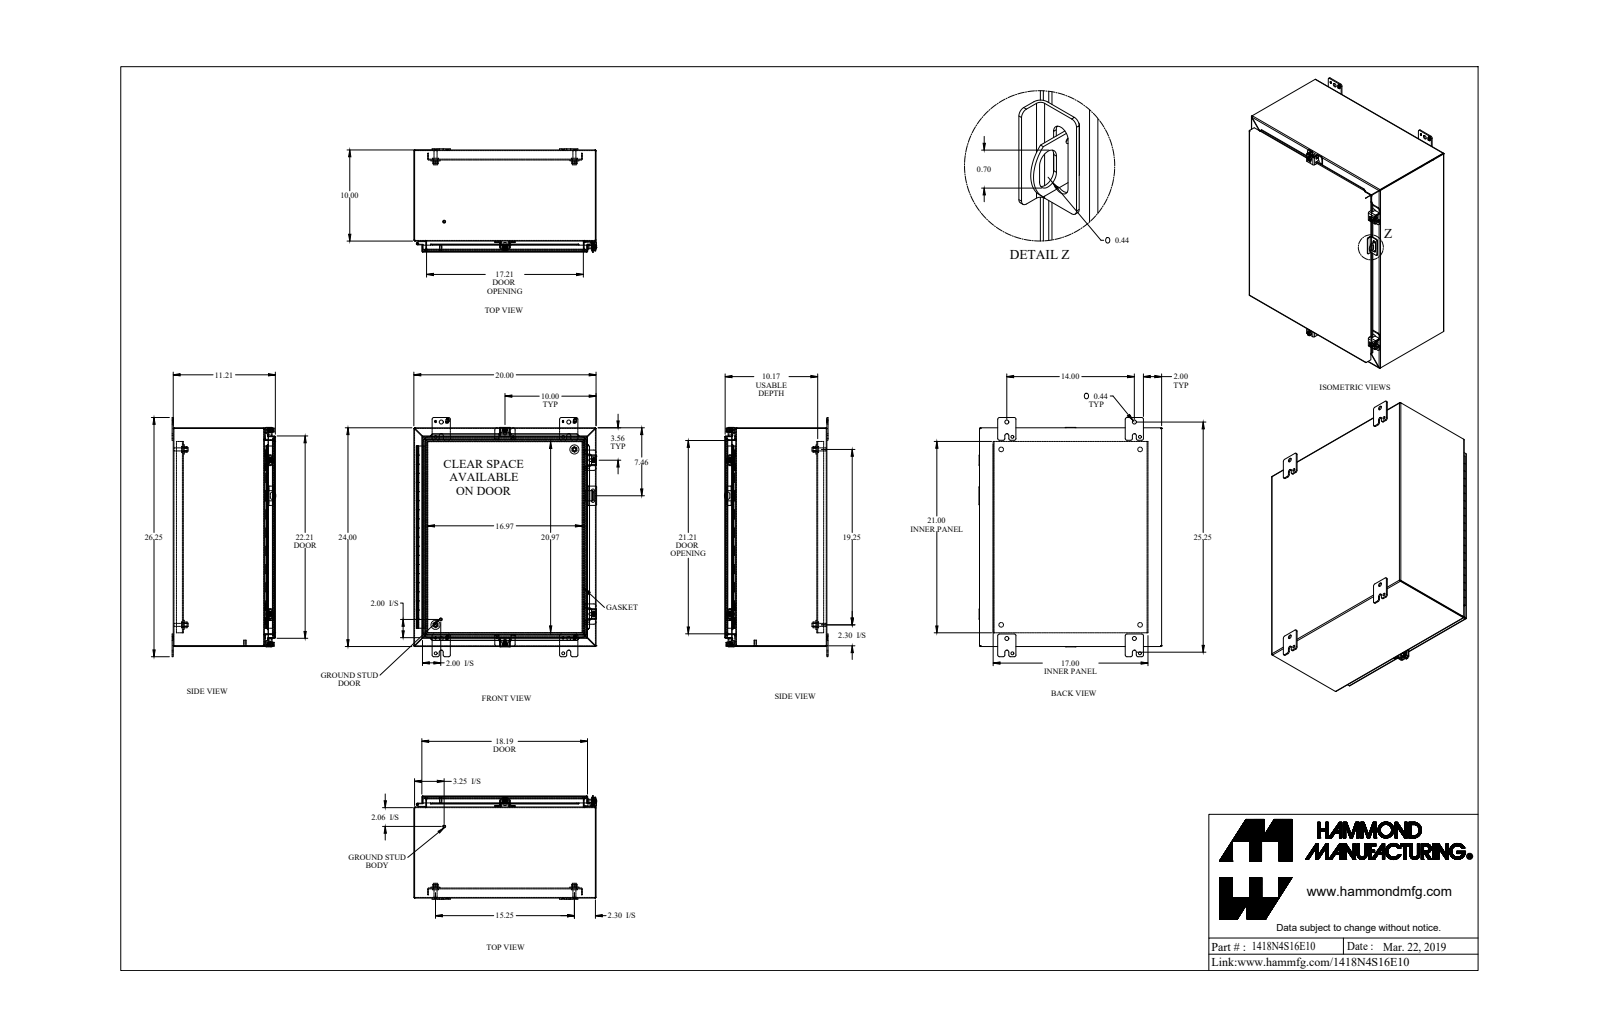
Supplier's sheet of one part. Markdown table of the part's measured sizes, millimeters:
| quantity | value |
| --- | --- |
| part name | 1418N4S16E10_Default |
| STEP written by | SolidWorks 2019 (CONFIG_CONTROL_DESIGN) |
| units | millimeters |
| bodies | 39 solids, 1374 faces (746 planar, 494 cylindrical, 134 other) |
| overall size | 666.8 × 509.6 × 288.9 |
| volume | 3 227 000 mm³ |
| surface area | 3 361 000 mm² |
| round holes (diameter × count) | 5.4 × 4, 8 × 4, 9.5 × 4, 11.1 × 4, 12.7 × 4, 6.7 × 2, 6.7 × 2, 7.8 × 2, 11.3 × 2, 2.8 × 1, 3.2 × 1 |
| round bosses / shafts (diameter × count) | 16.5 × 4, 12.7 × 4, 9.9 × 4, 9.5 × 4, 8.4 × 4, 6.2 × 4, 25.4 × 2, 8 × 2 |
| partial cylindrical surfaces (radius × count) | 4.8 × 26, 0.9 × 24, 2.7 × 24, 1.2 × 21, 3.6 × 21, 6.4 × 20, 3.2 × 12, 1.1 × 8 |
| main face-to-face distances | 1.8, 506.2, 281.1, 282.9, 1.8, 282.9, 284.7, 23.8, 607.8, 2.4 |
| hole center spacings | 201.1, 576.4, 355.6, 623.8, 44.1, 61.8, 373.4, 387.4 |
